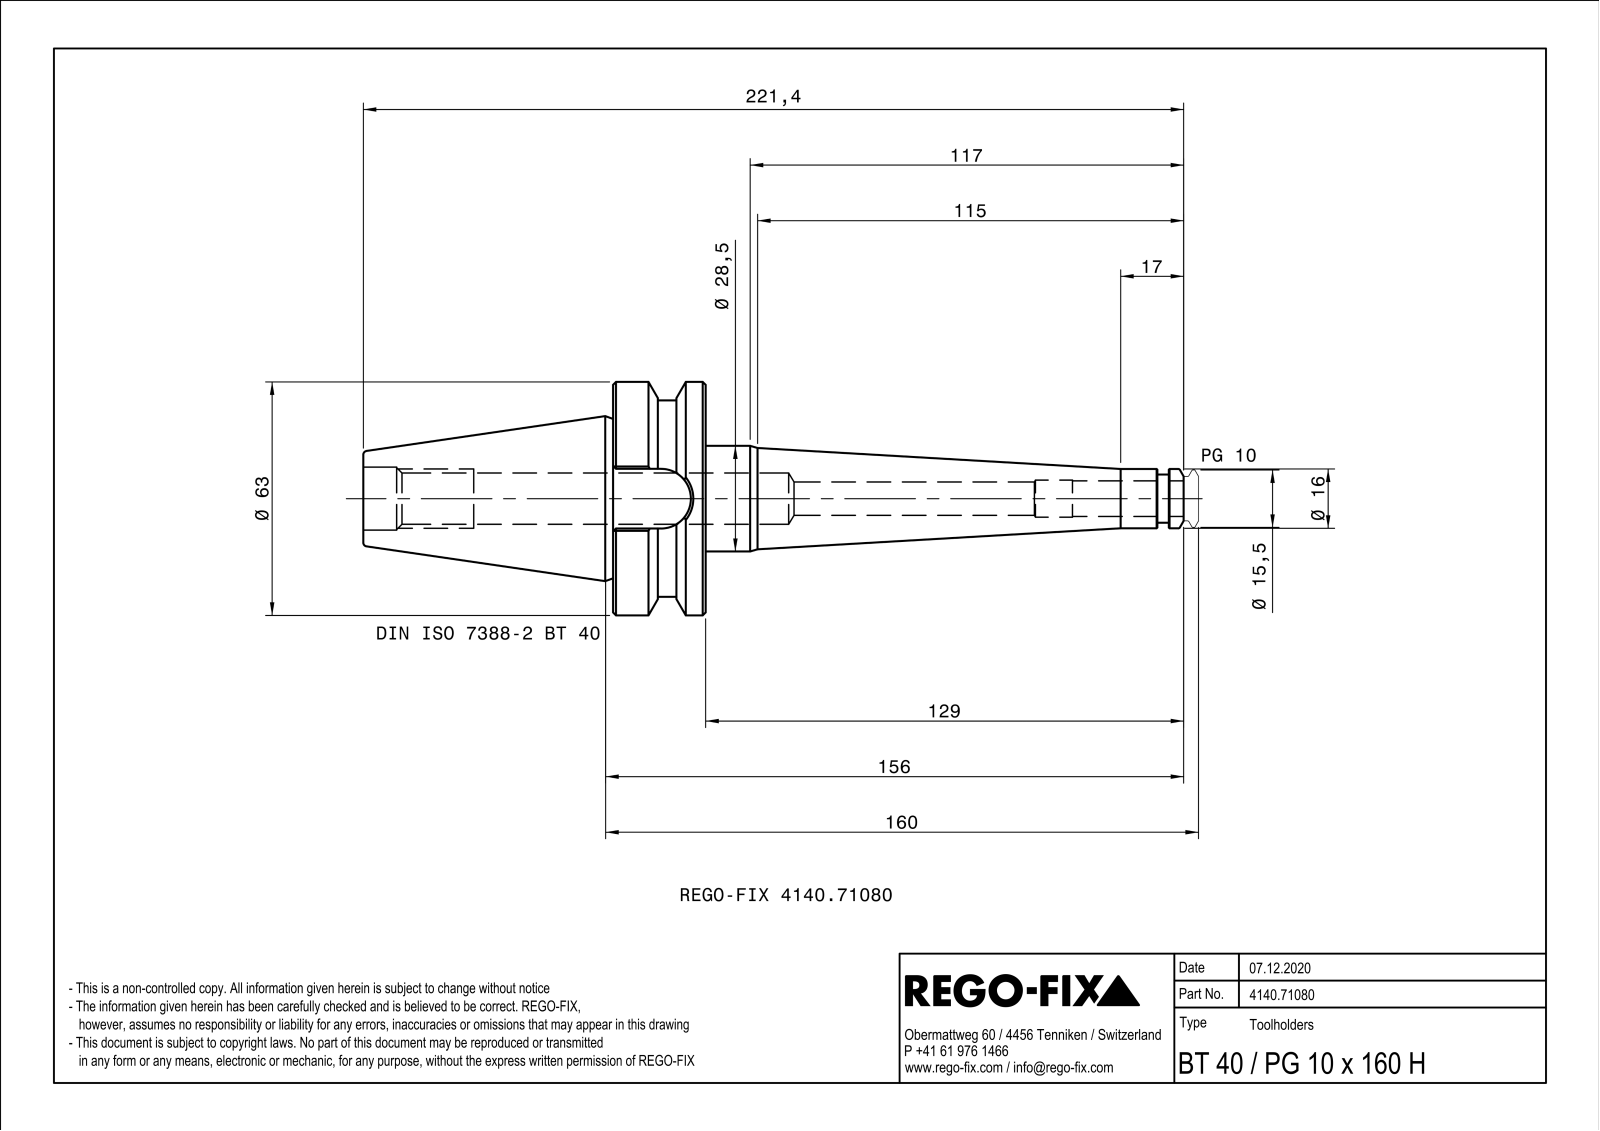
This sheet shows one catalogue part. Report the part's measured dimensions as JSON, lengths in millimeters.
{"part_name": "NOCUT", "step_written_by": "SIEMENS PLM Software Solid Edge ST10 (AUTOMOTIVE_DESIGN)", "units": "millimeters", "bodies": {"solids": 1, "faces": 104, "planar": 39, "cylindrical": 22, "other": 43}, "overall_size": [221.4, 63, 63], "volume_mm3": 156083, "surface_area_mm2": 34808, "round_holes": [[9, 1], [10, 1], [13.84, 1], [17, 1]], "round_bosses_or_shafts": [[63, 1], [53, 1], [28.5, 1], [16, 1], [13, 1]], "partial_cylinders_radius": [[0.5, 4], [8.05, 1]], "face_to_face_distances": [25, 45.1, 92.4, 67.4, 16.1, 3.1, 125, 150, 217.4, 121.9]}
